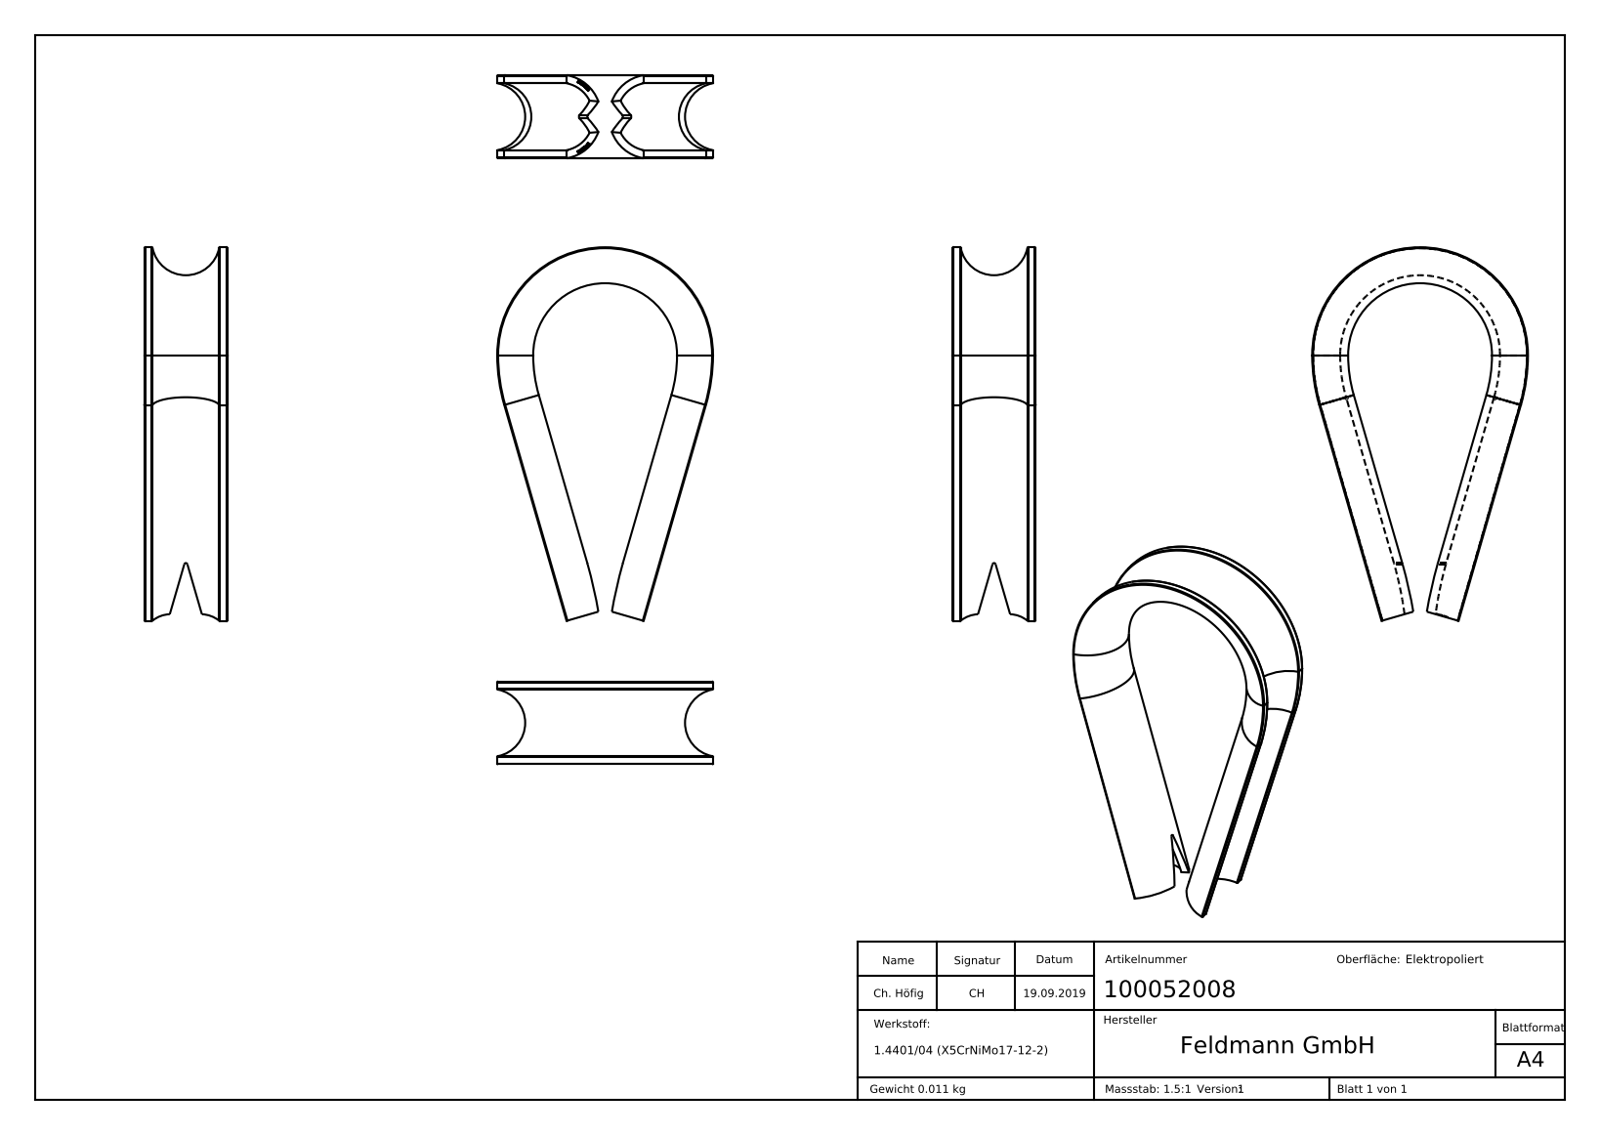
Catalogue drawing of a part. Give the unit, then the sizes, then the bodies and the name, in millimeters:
Units: millimetres
Overall size (bounding box): 46.75 × 27 × 10.36
Partial cylindrical surfaces — rounded edges, fillets, slot ends (radius × count): R0.1 ×8, R4.25 ×2, R5.25 ×2, R22.5 ×2, R0.2 ×1, R13.5 ×1
Volume: 1 336 mm³ · Surface area: 2 927 mm²
Bodies: 1 solid, 281 faces (111 planar, 22 cylindrical, 148 other)
Part name (STEP PRODUCT): 100052008
STEP written by: SolidWorks 2015 (CONFIG_CONTROL_DESIGN)
